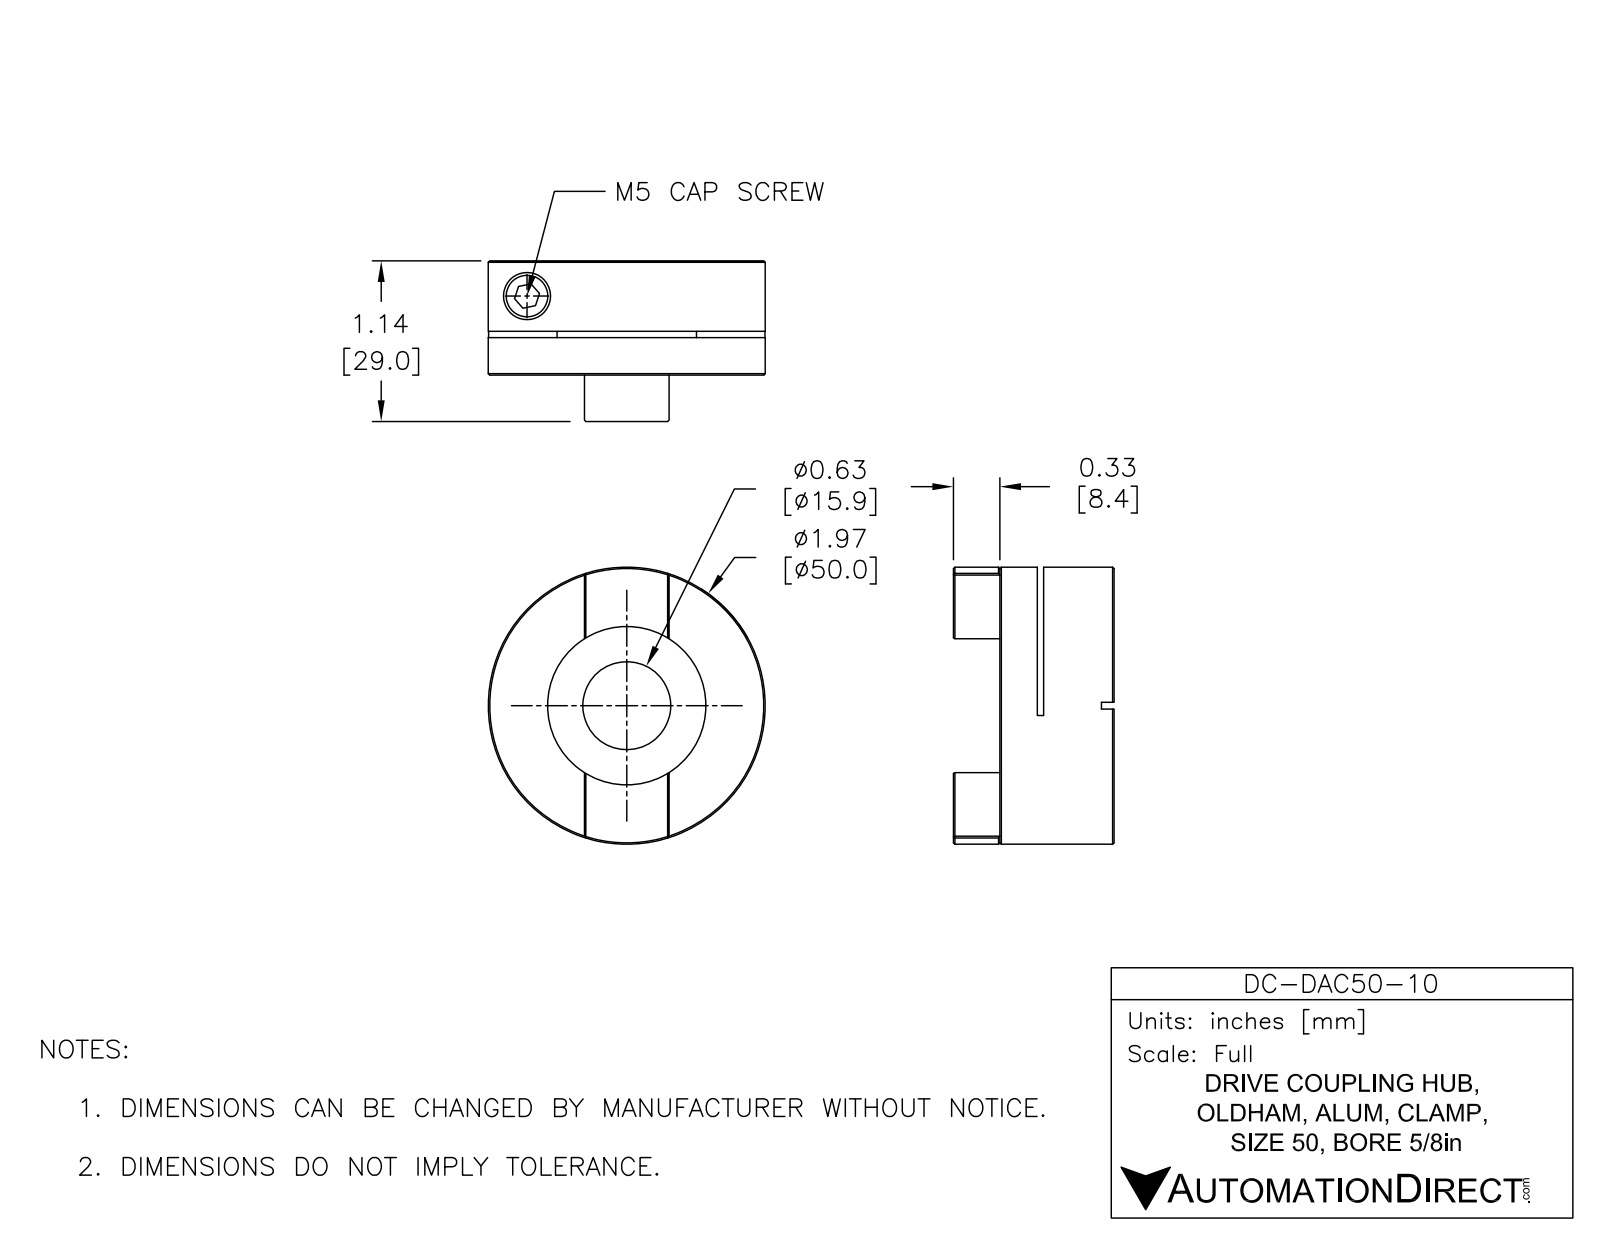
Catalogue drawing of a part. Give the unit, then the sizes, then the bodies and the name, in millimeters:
Units: millimetres
Overall size (bounding box): 50 × 50 × 28.98
Round holes (diameter × count): ⌀5.51 ×1, ⌀10.01 ×1, ⌀15.88 ×1, ⌀28.57 ×1
Round bosses / shafts (diameter × count): ⌀50 ×1
Partial cylindrical surfaces — rounded edges, fillets, slot ends (radius × count): R25.4 ×1
Main face-to-face distances: 20.6, 13.84, 6.76, 12.7, 1.14, 7.9, 18.82, 6.12, 4.98, 1.78
Volume: 35 286 mm³ · Surface area: 11 807 mm²
Bodies: 1 solid, 57 faces (30 planar, 17 cylindrical, 10 other)
Part name (STEP PRODUCT): DC-DAC50-10
STEP written by: SolidWorks 2015 (AUTOMOTIVE_DESIGN)
